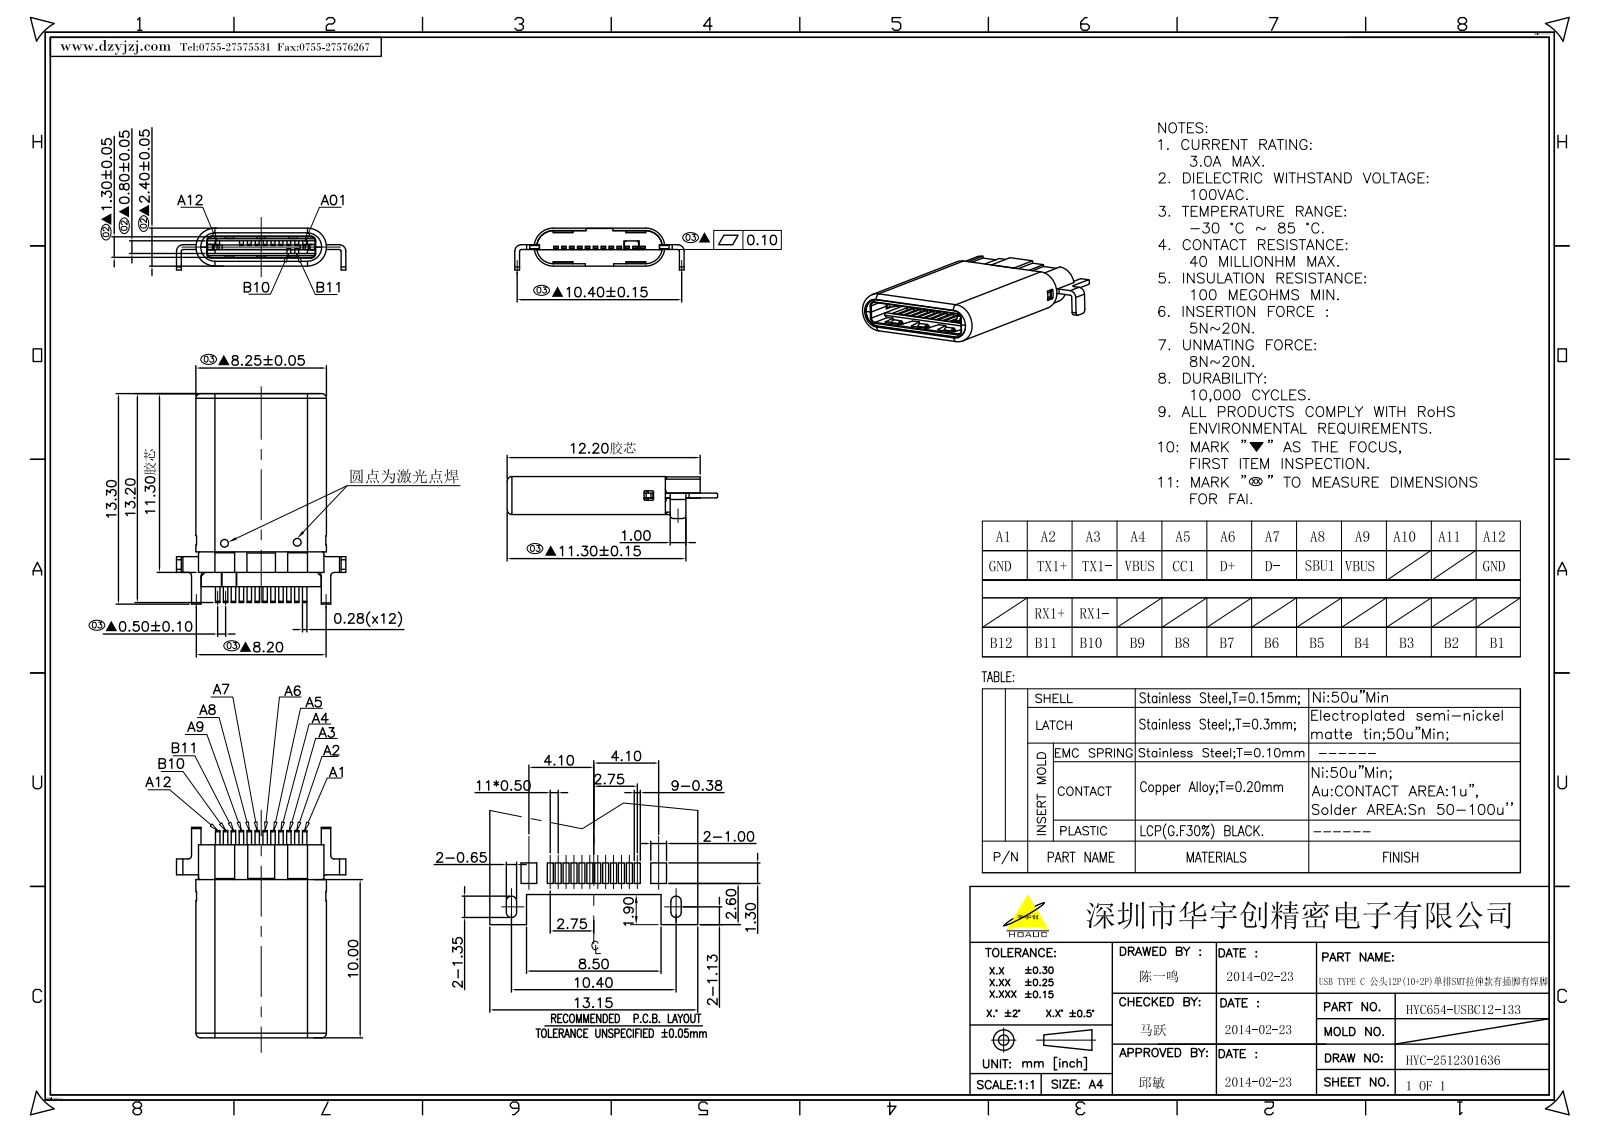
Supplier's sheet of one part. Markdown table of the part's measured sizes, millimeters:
| quantity | value |
| --- | --- |
| part name | TANPIAN-PLASTIC_1_2__2_5_1_1__5 |
| STEP written by | CREO PARAMETRIC BY PTC INC, 2022073 (AUTOMOTIVE_DESIGN) |
| units | millimeters |
| bodies | 1 solid, 429 faces (337 planar, 86 cylindrical, 6 other) |
| overall size | 13.3 × 10.7 × 2.65 |
| volume | 182 mm³ |
| surface area | 430 mm² |
| round holes (diameter × count) | 0.5 × 2 |
| partial cylindrical surfaces (radius × count) | 0.1 × 8, 0.3 × 8, 0.25 × 6, 0.15 × 4, 0.2 × 4, 1.05 × 4, 0.4 × 2, 0.58 × 2 |
| main face-to-face distances | 0.8, 2.4, 1.6, 1.05, 0.55, 1.35, 0.5, 1.85, 1.04, 0.56 |
| hole center spacings | 4.6 |
